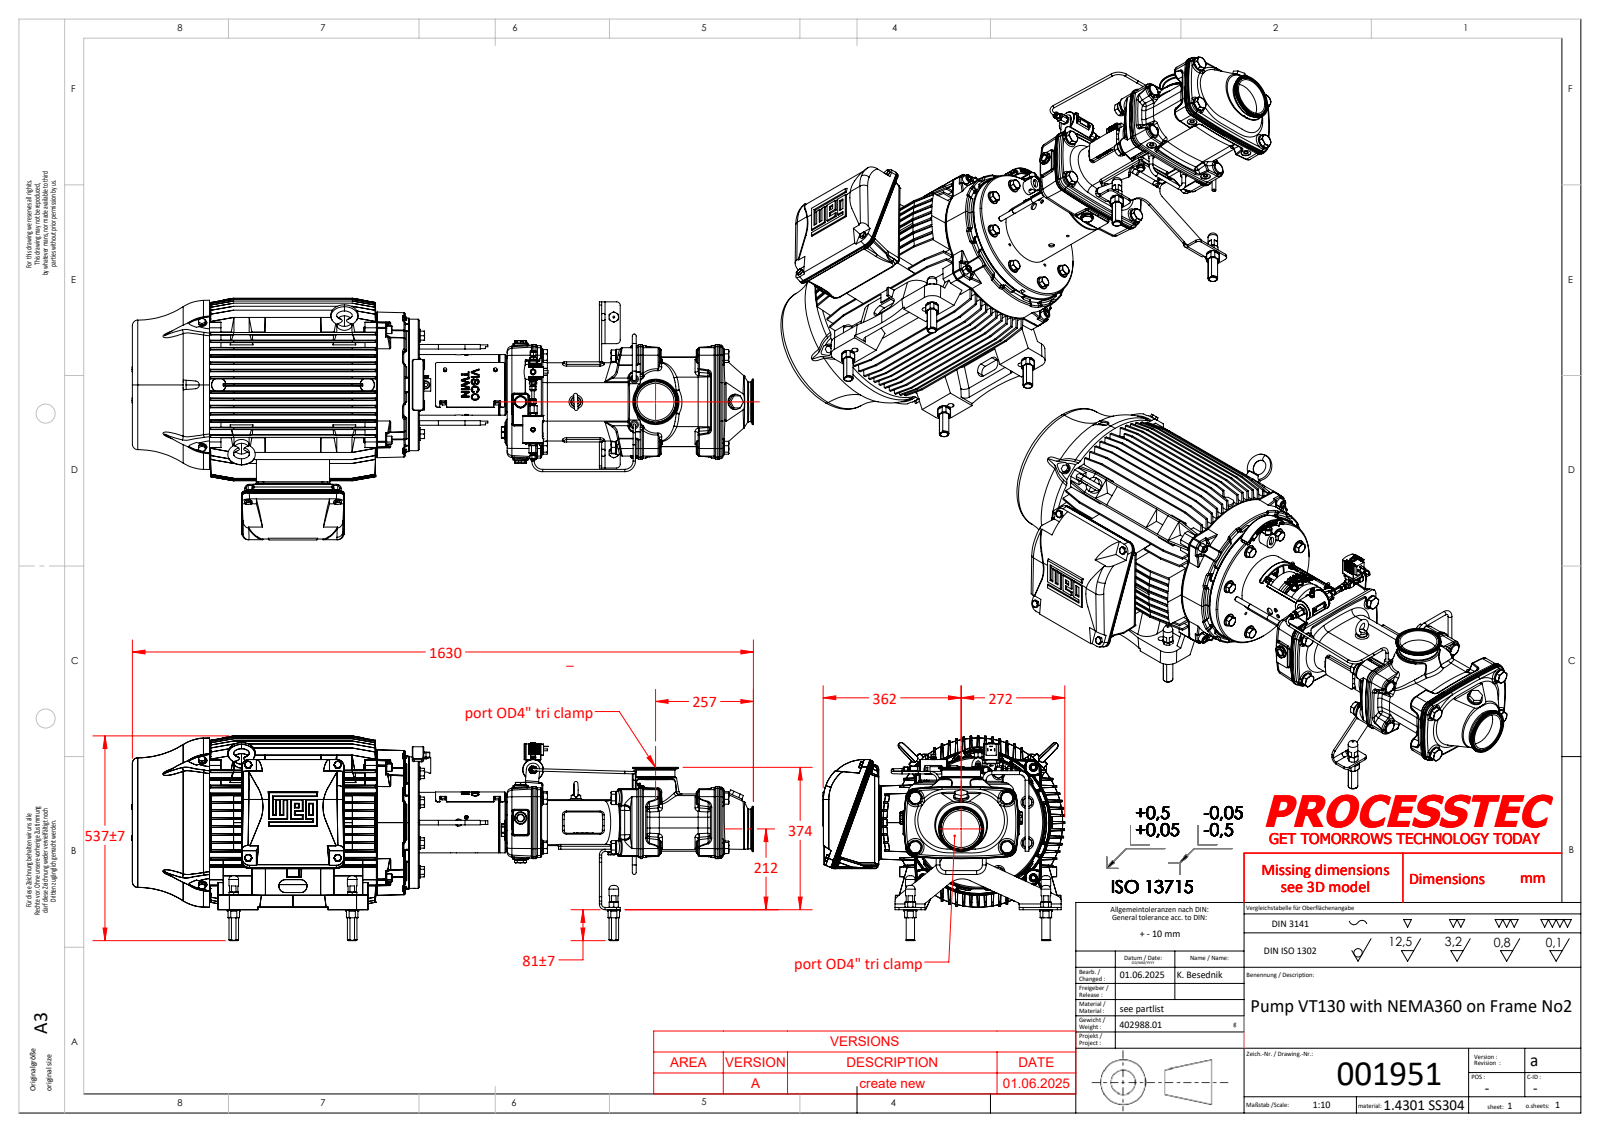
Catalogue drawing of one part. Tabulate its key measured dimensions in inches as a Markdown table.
| quantity | value |
| --- | --- |
| part name | 001381; Hex Bolt ANSI 0.625-11x2x1p5_HBOLT 0.6250-11x2x1.5-N; 001946_38,4; 001008 (+8 more) |
| STEP written by | SolidWorks 2023 (AUTOMOTIVE_DESIGN) |
| units | inches |
| bodies | 191 solids, 14611 faces (4868 planar, 2967 cylindrical, 6776 other) |
| overall size | 64.217 × 24.973 × 21.146 |
| volume | 14 550 in³ |
| surface area | 17 170 in² |
| round holes (diameter × count) | 0.268 × 17, 0.335 × 14, 0.315 × 13, 0.551 × 12, 0.669 × 9, 0.689 × 9, 0.984 × 9, 0.531 × 8, 0.656 × 8, 0.656 × 8, 0.66 × 8, 0.205 × 6 |
| round bosses / shafts (diameter × count) | 0.315 × 20, 0.394 × 16, 0.236 × 13, 1.312 × 8, 0.625 × 8, 0.472 × 8, 0.197 × 8, 0.984 × 7 |
| partial cylindrical surfaces (radius × count) | 0.118 × 92, 0.059 × 49, 0.079 × 37, 0.157 × 37, 0.126 × 33, 0.236 × 23, 0.591 × 22, 0.087 × 20 |
| main face-to-face distances | 17.244, 0.74, 0.75, 5.22, 2.219, 5.941, 7.458, 0.72, 2.238, 0.739 |
| hole center spacings | 2.165, 5.091, 5.5, 7.778, 10.163, 3.365, 4.006, 4.521 |
